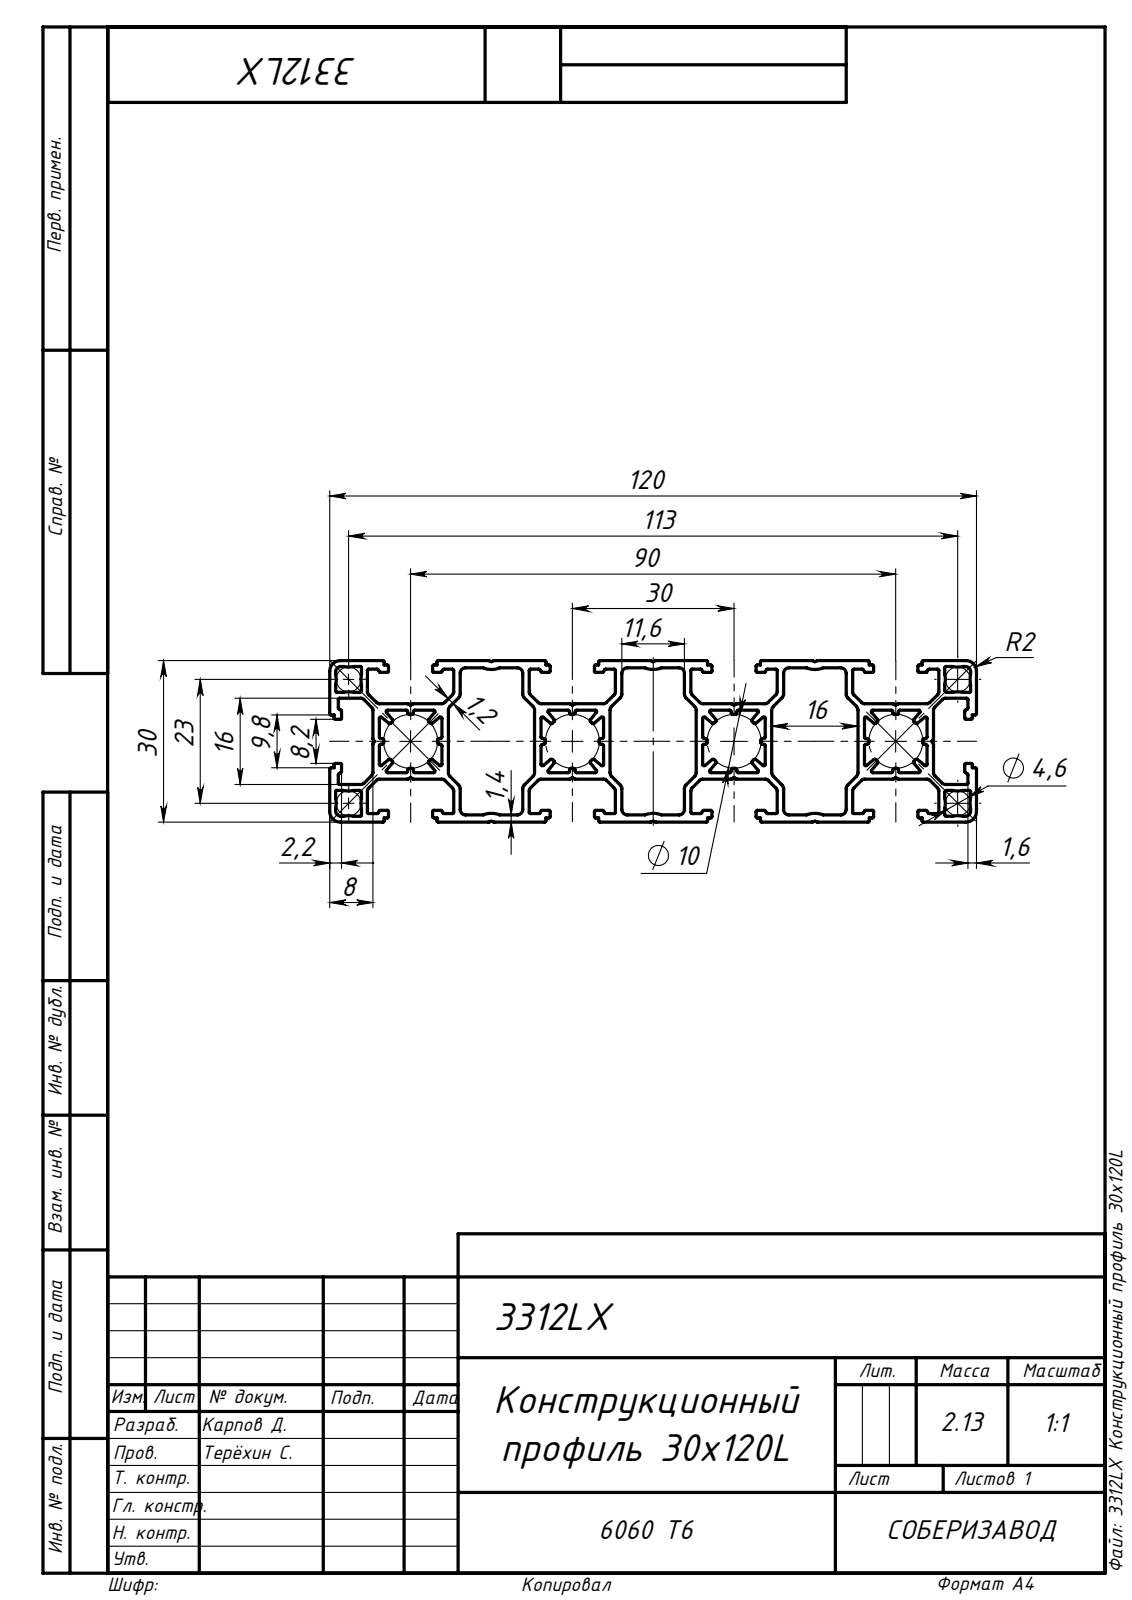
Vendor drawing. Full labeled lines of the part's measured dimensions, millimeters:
STEP written by: SolidWorks 2019 (AUTOMOTIVE_DESIGN)
Units: millimetres
Bodies: 1 solid, 898 faces (404 planar, 494 cylindrical, 0 other)
Overall size (bounding box): 1000 × 120 × 30
Volume: 789 503 mm³ · Surface area: 1 162 000 mm²
Partial cylindrical surfaces — rounded edges, fillets, slot ends (radius × count): R0.25 ×288, R0.75 ×40, R1 ×40, R5.05 ×16, R4 ×6, R0.4 ×4, R2 ×4, R5 ×4
Main face-to-face distances: 30, 15, 14, 22, 8, 1, 45, 60, 16, 20.8
